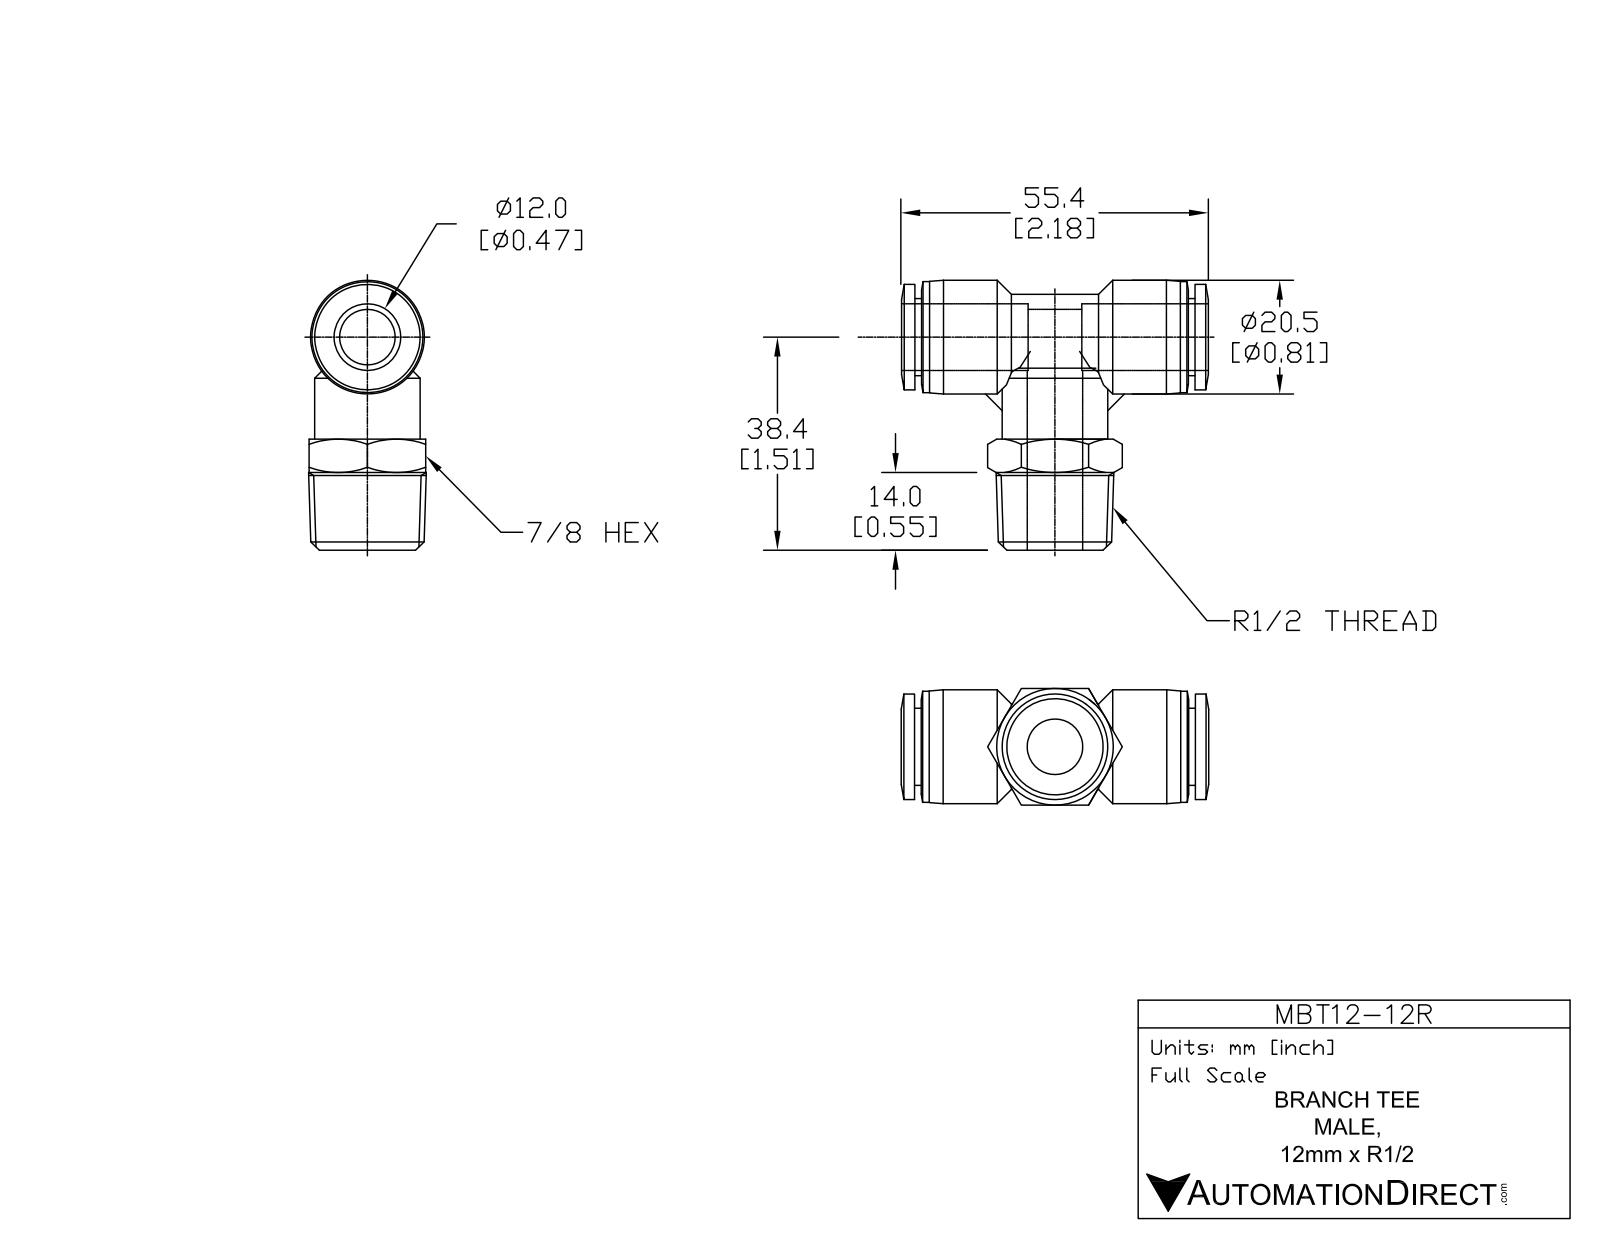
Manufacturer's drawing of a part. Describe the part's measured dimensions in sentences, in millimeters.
The part is named "MBT12M-12R". Its 3-D file was written by "SolidWorks 2015 (AUTOMOTIVE_DESIGN)". It is 1 solid with 98 faces: 24 planar, 32 cylindrical and 42 other. Overall it measures 57.3 by 48.6 by 21 millimeters. Its volume is 16 700 cubic millimeters and its surface area 9 639 square millimeters. Round holes: 2 of diameter 10, 1 of diameter 12.3. Round bosses or shafts: 2 of diameter 19, 1 of diameter 20.5, 1 of diameter 20, 1 of diameter 15.4, 1 of diameter 13.9. Partial cylindrical surfaces (rounded edges, fillets, slot ends): 1 of radius 7.7. The main face-to-face distances are 21, 1.2, 51.3, 52.5, 20.5, 32, 19.3, 30.8, 50.1, 20.
